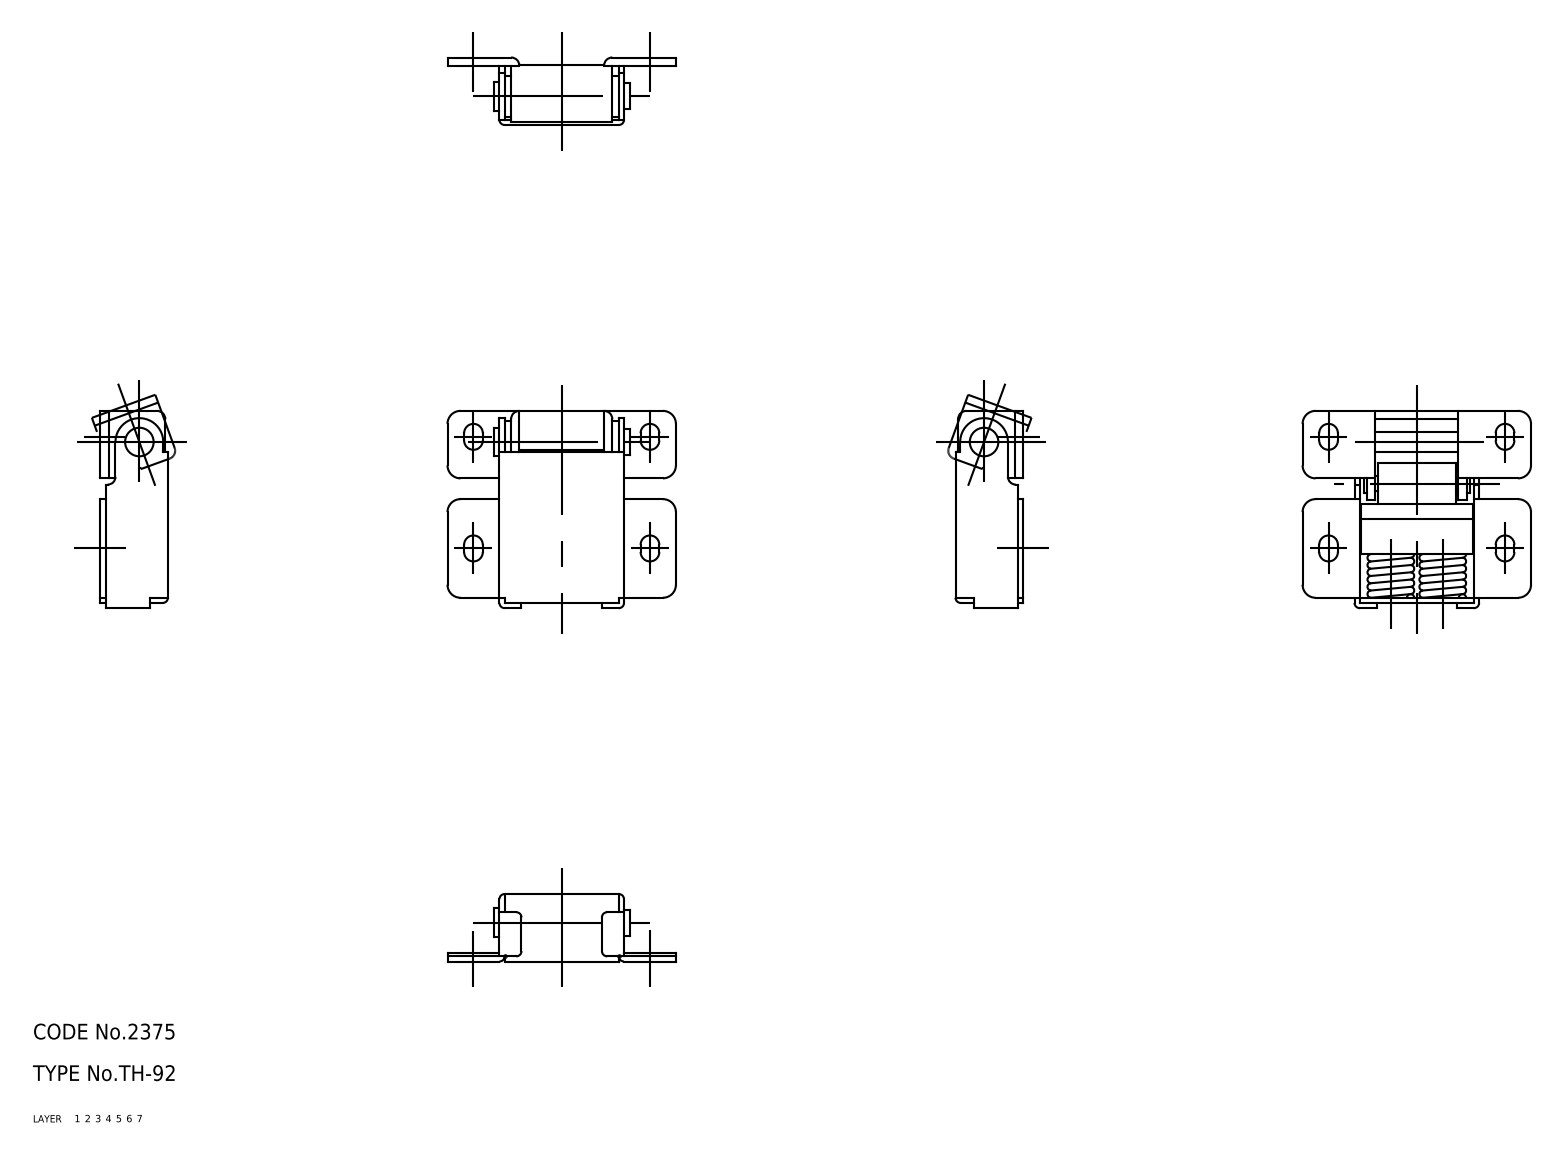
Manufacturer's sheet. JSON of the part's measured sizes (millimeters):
{"part_name": "spring; washer; spring holder; shaft_B (+5 more)", "step_written_by": "CADfix (AUTOMOTIVE_DESIGN)", "units": "millimeters", "bodies": {"solids": 10, "faces": 196, "planar": 0, "cylindrical": 0, "other": 196}, "overall_size": [44, 38, 13], "volume_mm3": 6320, "surface_area_mm2": 10522}
